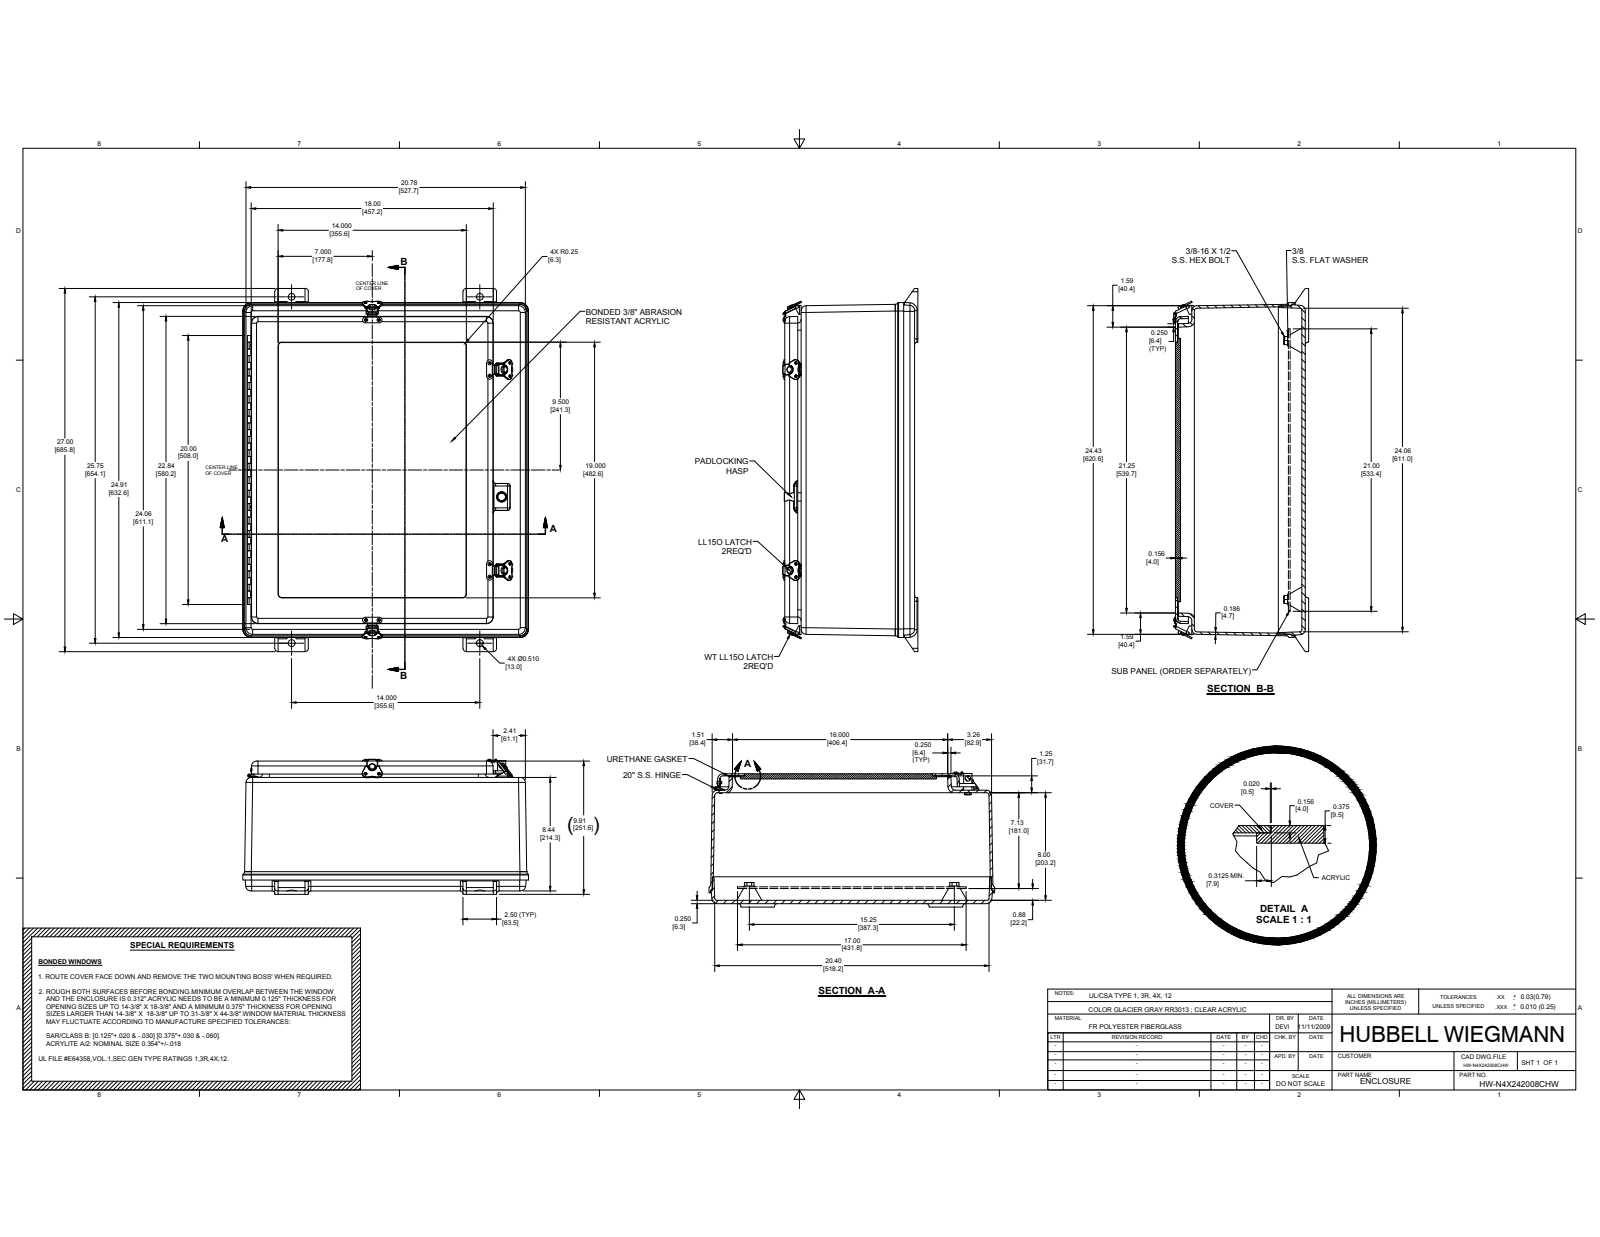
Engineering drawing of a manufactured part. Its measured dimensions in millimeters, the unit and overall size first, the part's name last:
Units: millimetres
Overall size (bounding box): 685.8 × 539.75 × 255.39
Round holes (diameter × count): ⌀3.3 ×32, ⌀1.59 ×16, ⌀1.65 ×8, ⌀3.5 ×8, ⌀4.76 ×8, ⌀7.8 ×4, ⌀14.3 ×4, ⌀3.43 ×3, ⌀3.97 ×3, ⌀12.7 ×2, ⌀12.96 ×2, ⌀3.17 ×1
Round bosses / shafts (diameter × count): ⌀3.56 ×16, ⌀7.54 ×8, ⌀12.7 ×4, ⌀5.08 ×3, ⌀6.35 ×1, ⌀5.11 ×1
Partial cylindrical surfaces — rounded edges, fillets, slot ends (radius × count): R0.25 ×101, R6.35 ×28, R4.76 ×21, R0.76 ×16, R7.94 ×16, R9.53 ×16, R12.7 ×12, R1.59 ×10
Main face-to-face distances: 6.35, 4.72, 245.31, 238.96, 235.79, 229.44, 9.52, 4.73, 3.96, 241.35
Hole centre spacings: 165.1, 304.8, 19.08, 23.81, 25.4, 38.4, 84.06, 379.42
Volume: 7 751 000 mm³ · Surface area: 2 865 000 mm²
Bodies: 59 solids, 1592 faces (617 planar, 614 cylindrical, 361 other)
Part name (STEP PRODUCT): WPN2420B; WPN24208SHWT; SS HINGE COVER (20); 0.13 RIVET PIN (+7 more)
STEP written by: Autodesk Inventor 2014 (AUTOMOTIVE_DESIGN)
